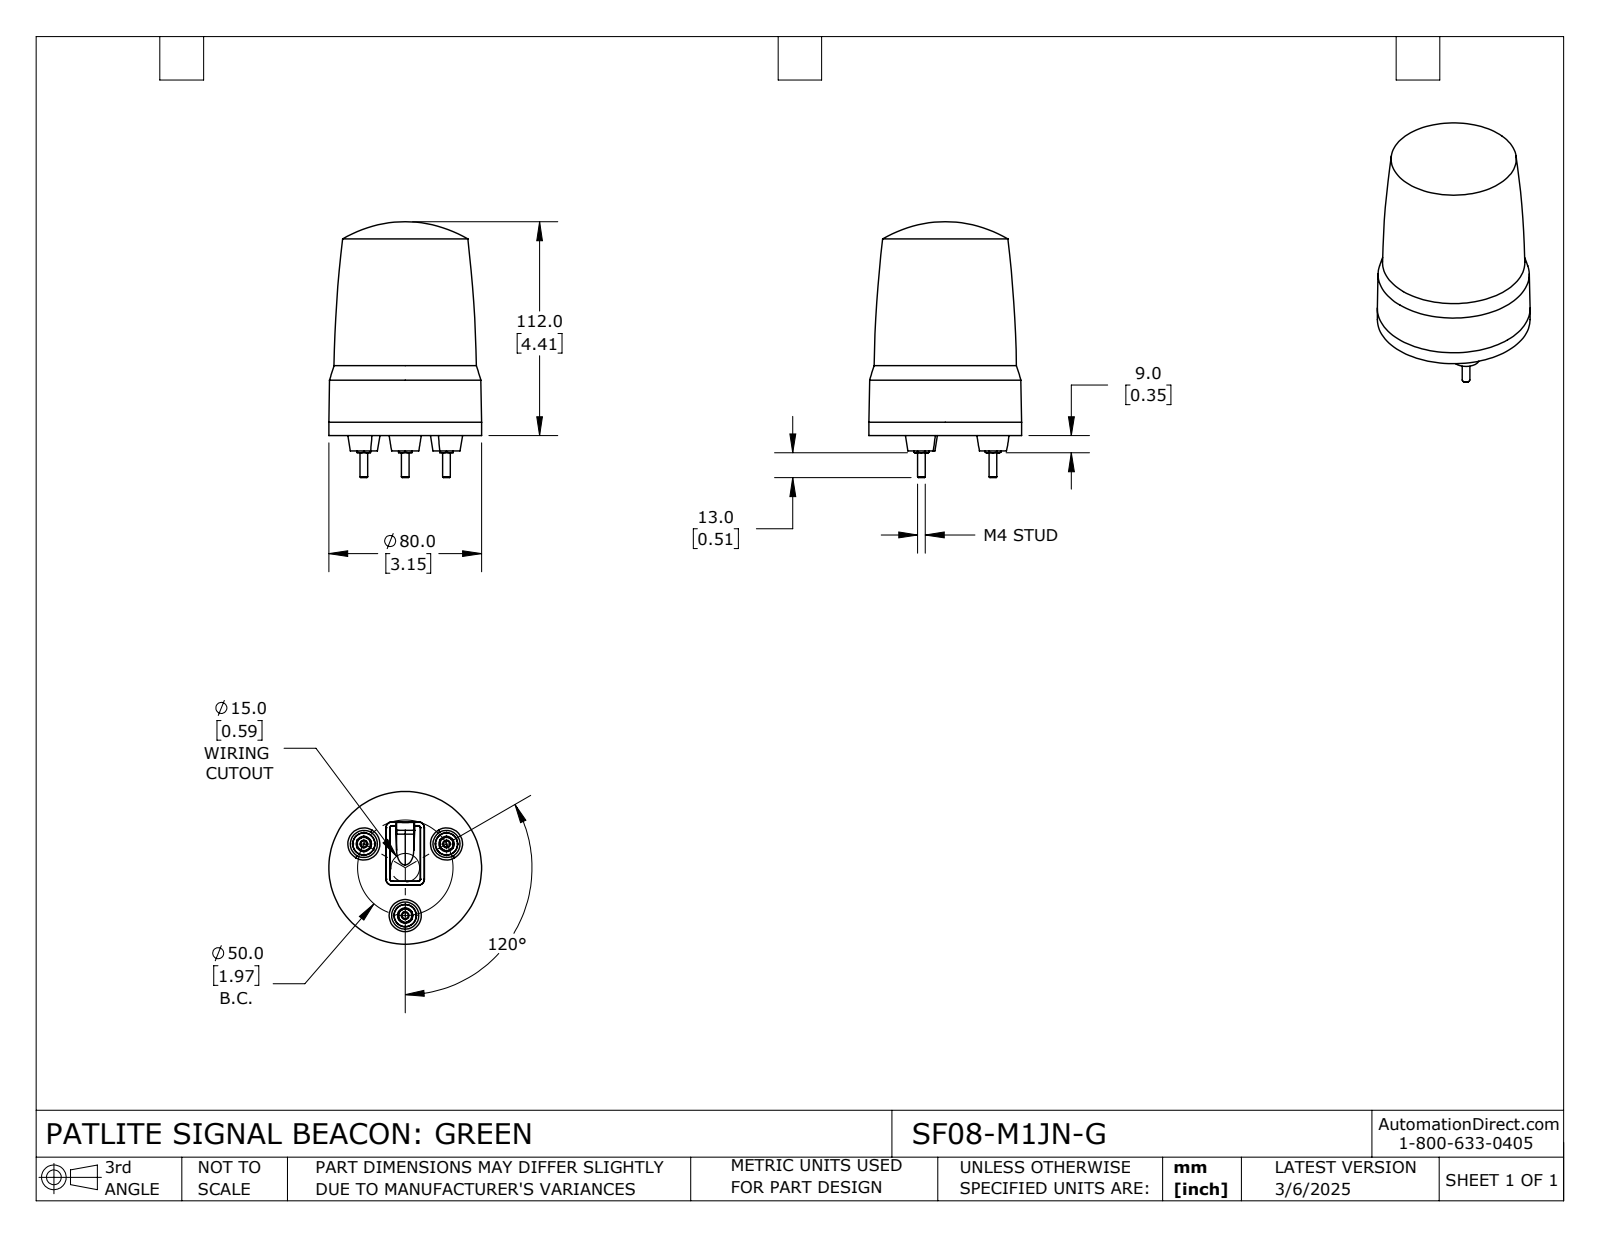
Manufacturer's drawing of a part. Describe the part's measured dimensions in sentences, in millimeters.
The part is named "SF08-M1JN-G". Its 3-D file was written by "SolidWorks 2024 (CONFIG_CONTROL_DESIGN)". It is 1 solid with 138 faces: 47 planar, 14 cylindrical and 77 other. Overall it measures 134 by 80 by 80 millimeters. Its volume is 463 225 cubic millimeters and its surface area 35 408 square millimeters. Round bosses or shafts: 3 of diameter 8, 3 of diameter 4, 1 of diameter 80. The main face-to-face distances are 0.85, 2.45, 1.6, 5.3, 6.15, 7.75, 2.7, 8, 8.85, 10.45.
